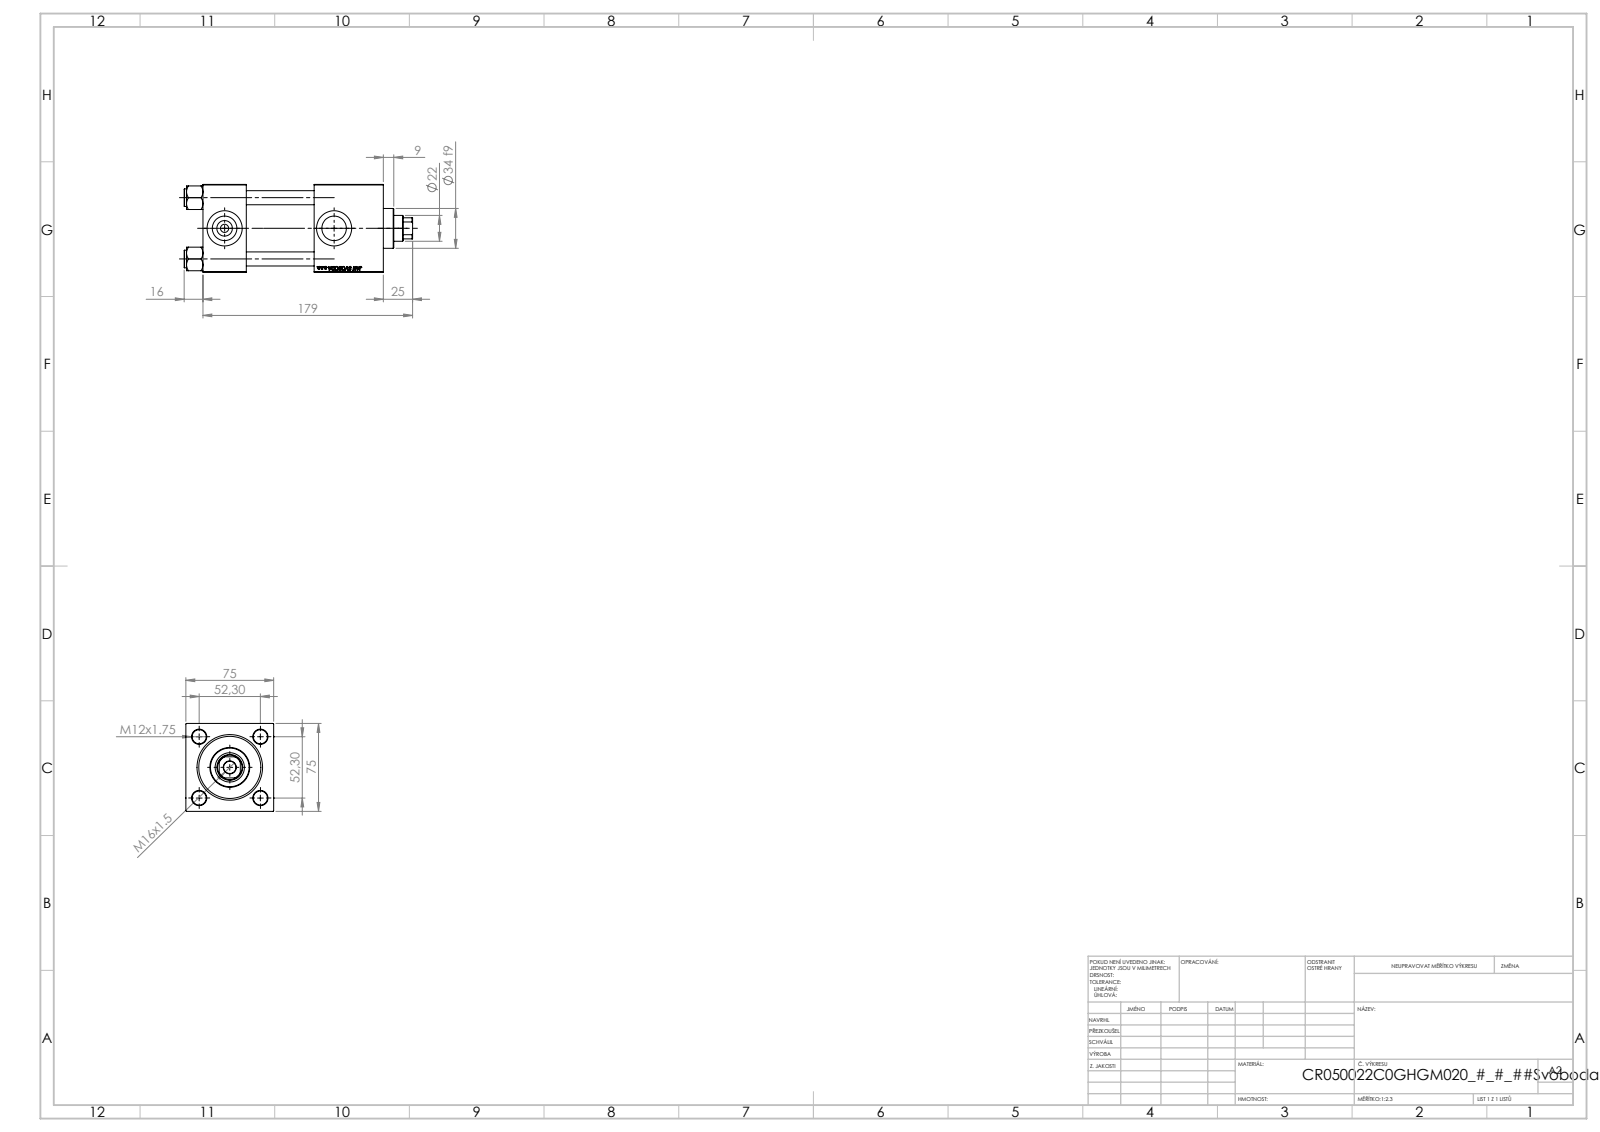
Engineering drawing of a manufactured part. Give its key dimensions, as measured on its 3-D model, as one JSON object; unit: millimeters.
{"part_name": "V215_VC_A; V215CR_C_Body; NUT_M5_C; V215CR_C_TYCINKA (+1 more)", "step_written_by": "SolidWorks 2019 (CONFIG_CONTROL_DESIGN)", "units": "millimeters", "bodies": {"solids": 11, "faces": 1148, "planar": 526, "cylindrical": 86, "other": 536}, "overall_size": [195, 75.54, 75], "volume_mm3": 656964, "surface_area_mm2": 147285, "round_holes": [[12, 4], [7, 2], [20.96, 2], [30, 2], [10.5, 1], [22, 1], [25, 1], [41, 1], [50, 1], [53, 1]], "round_bosses_or_shafts": [[15, 4], [56, 1], [34, 1]], "partial_cylinders_radius": [[10.5, 1]], "face_to_face_distances": [75, 37, 154, 117, 95, 58, 59, 125.3, 88.3, 30.3], "hole_center_spacings": [36.98, 52.3, 73.96, 93.5]}
